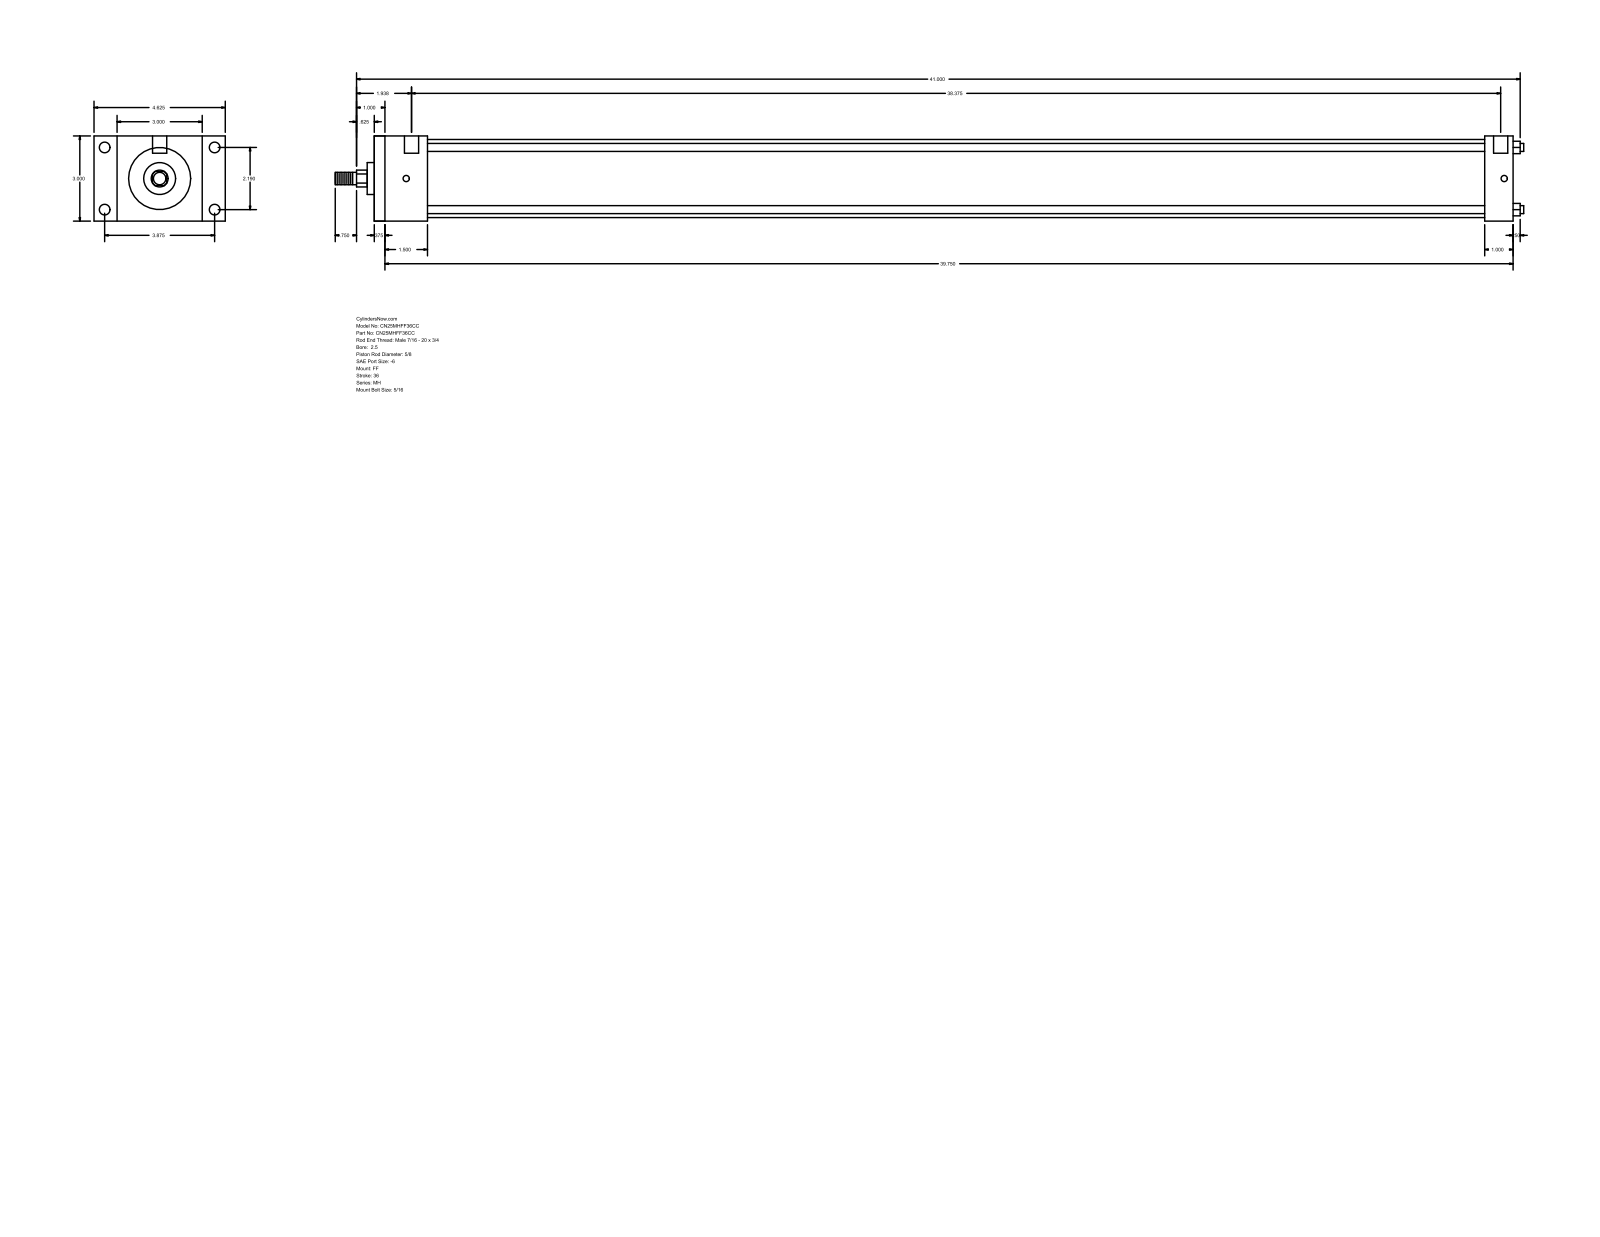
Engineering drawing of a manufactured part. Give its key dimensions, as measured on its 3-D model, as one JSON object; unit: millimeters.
{"part_name": "MH_FF__0250_0.625", "step_written_by": "GSSL Pune (CONFIG_CONTROL_DESIGN)", "units": "millimeters", "bodies": {"solids": 0, "faces": 92, "planar": 64, "cylindrical": 28, "other": 0}, "overall_size": [1063.62, 117.47, 76.2], "round_holes": [[5.56, 4], [9.53, 4], [12.7, 2]], "round_bosses_or_shafts": [[7.14, 4], [69.85, 1], [28.57, 1], [15.88, 1], [11.11, 1]], "partial_cylinders_radius": [[7.54, 1]], "face_to_face_distances": [76.2, 1019.17, 1009.65, 9.52, 25.4, 47.62, 993.77, 38.1, 984.25, 946.15], "hole_center_spacings": [55.62, 98.42, 113.05, 982.66, 3.17, 4.76, 974.73, 977.9]}
